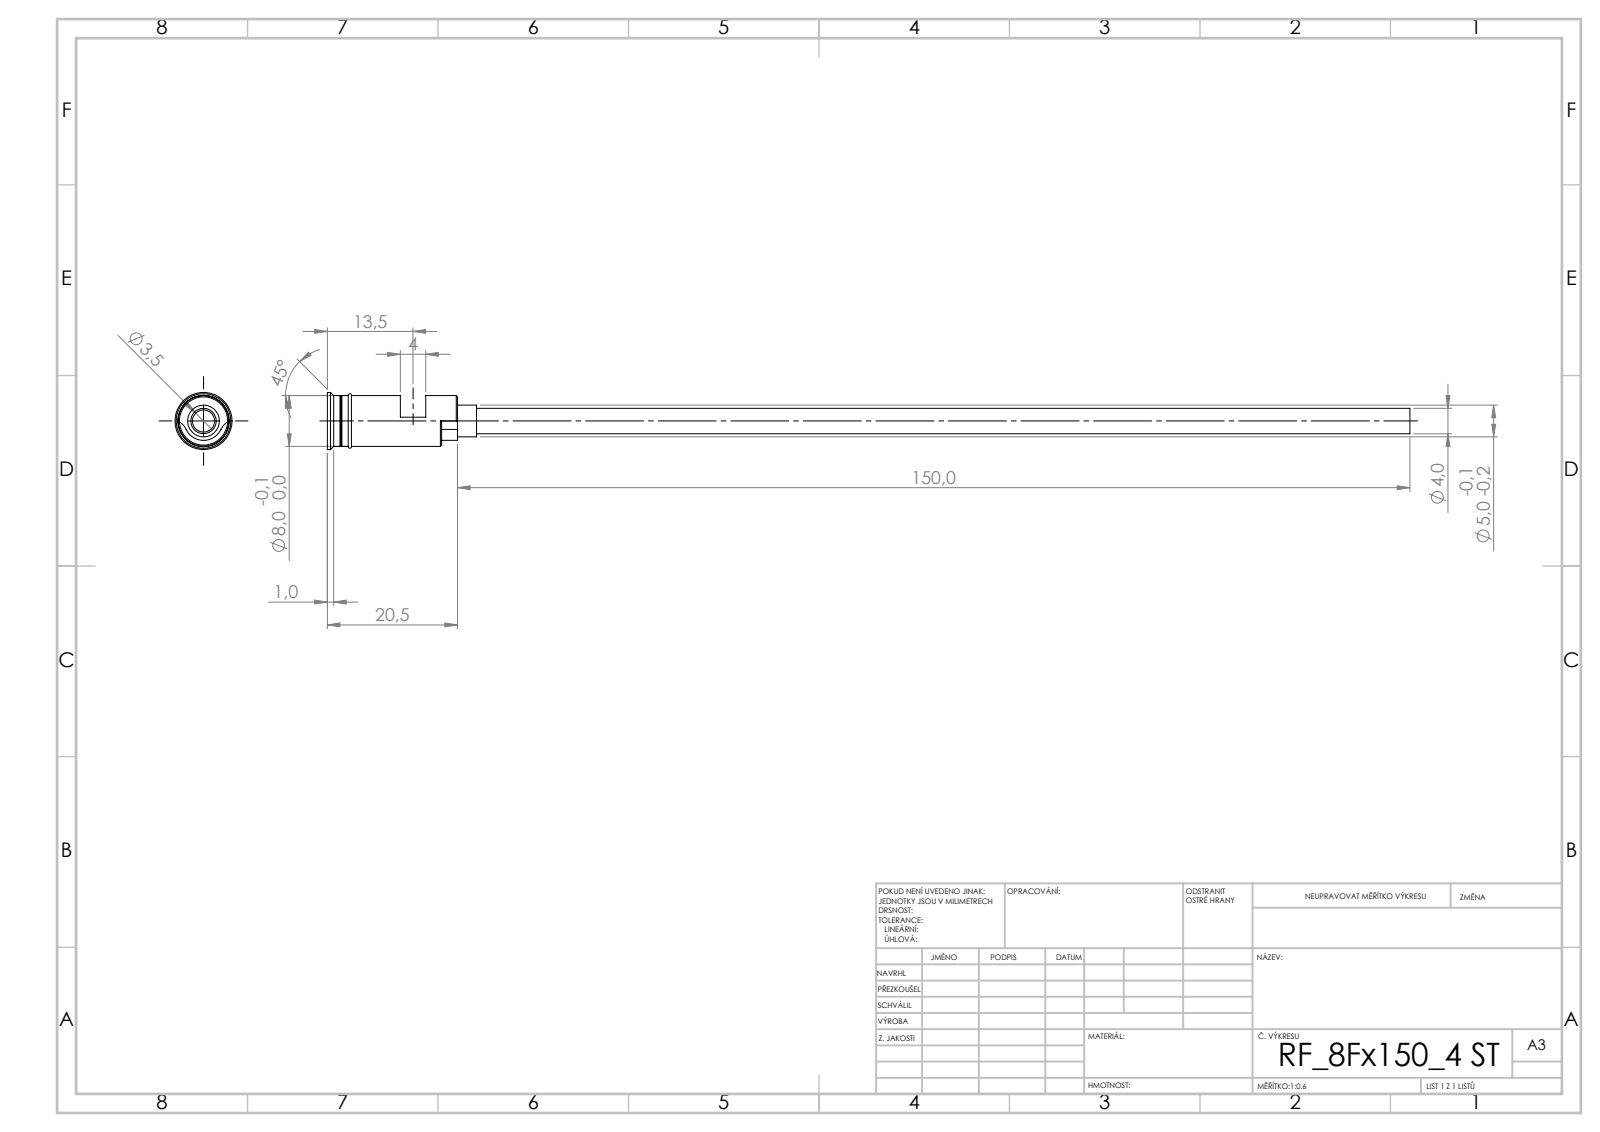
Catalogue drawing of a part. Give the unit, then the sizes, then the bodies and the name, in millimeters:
Units: millimetres
Overall size (bounding box): 170.5 × 9 × 9
Round holes (diameter × count): ⌀3.5 ×1
Round bosses / shafts (diameter × count): ⌀9 ×1, ⌀8 ×1, ⌀7.8 ×1, ⌀5 ×1, ⌀4 ×1
Partial cylindrical surfaces — rounded edges, fillets, slot ends (radius × count): R3 ×2, R3.05 ×1
Main face-to-face distances: 4, 11.5, 9, 20.5, 5, 15.5, 2.5, 18.5, 13.5, 9.5
Volume: 1 296 mm³ · Surface area: 4 303 mm²
Bodies: 1 solid, 55 faces (24 planar, 19 cylindrical, 12 other)
STEP written by: SolidWorks 2019 (CONFIG_CONTROL_DESIGN)
